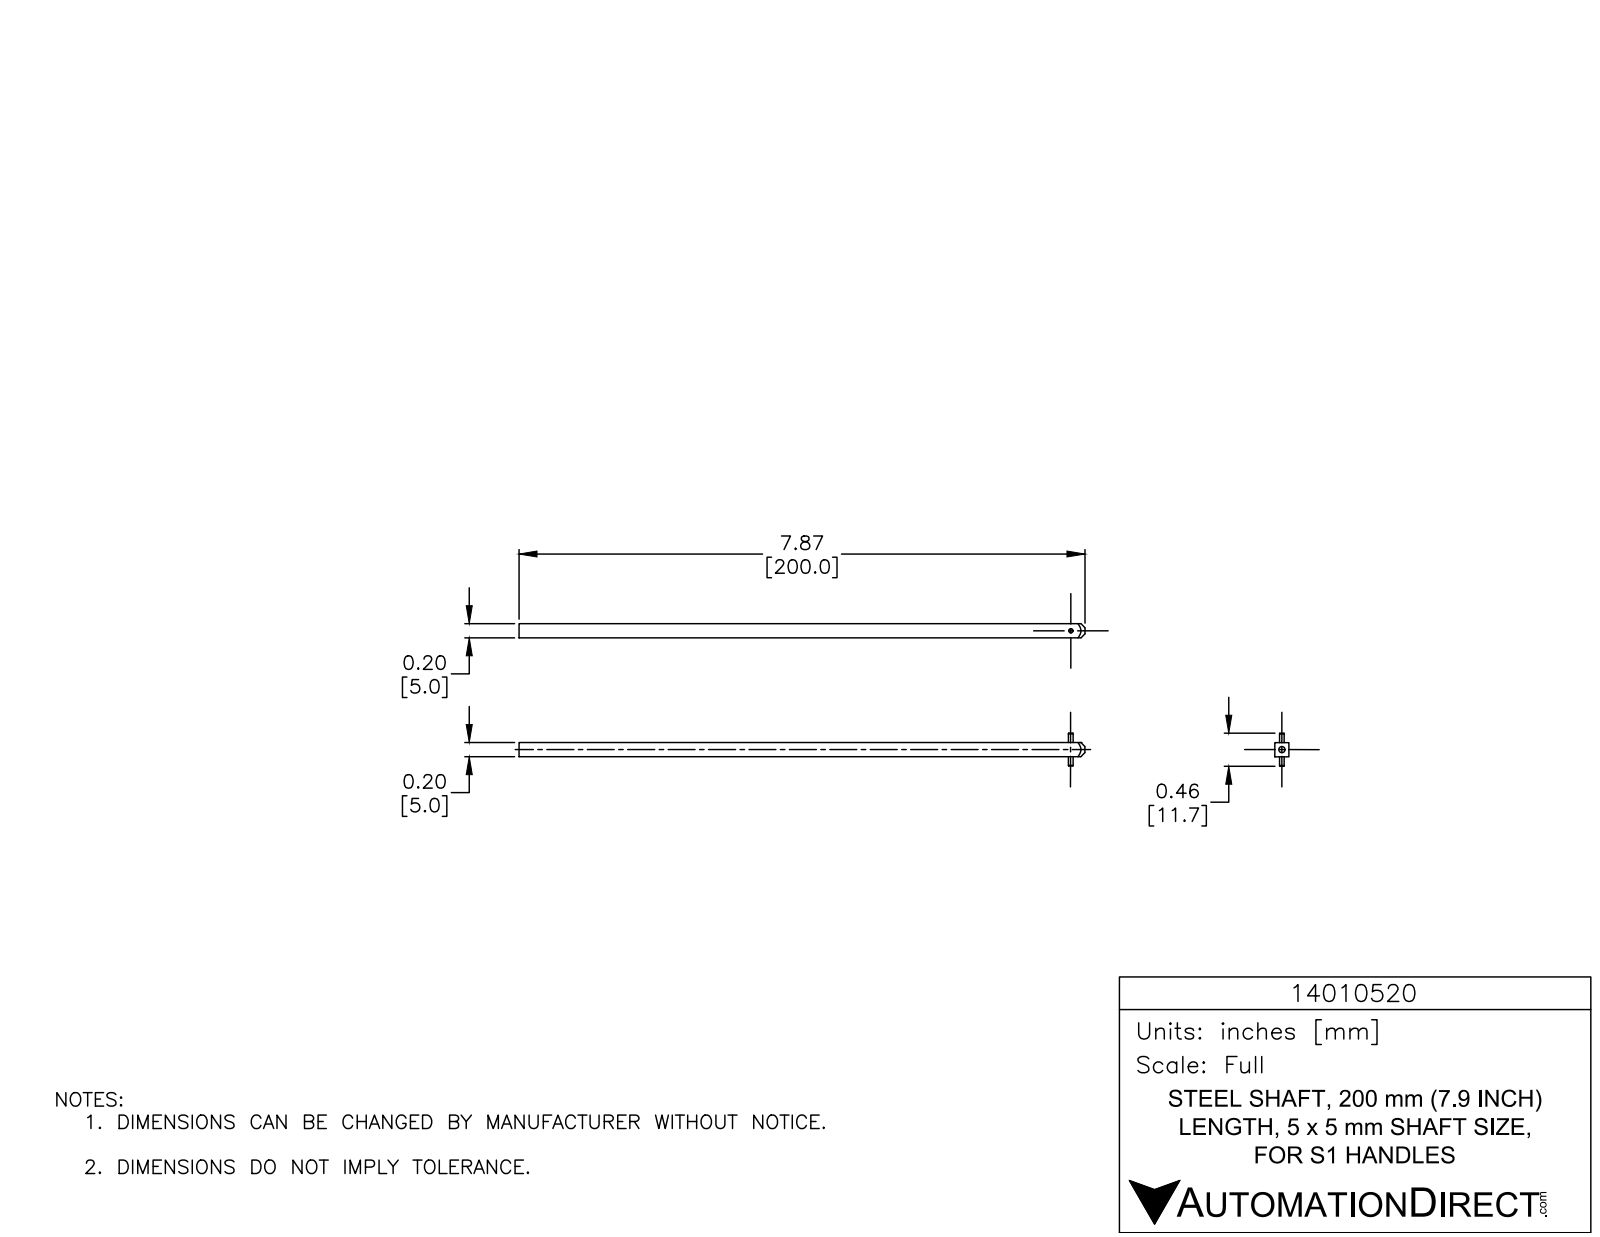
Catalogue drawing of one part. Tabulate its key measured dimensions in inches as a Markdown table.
| quantity | value |
| --- | --- |
| part name | 14010520 |
| STEP written by | SolidWorks 2015 (AUTOMOTIVE_DESIGN) |
| units | inches |
| bodies | 1 solid, 72 faces (35 planar, 24 cylindrical, 13 other) |
| overall size | 7.874 × 0.787 × 0.677 |
| volume | 0.695 in³ |
| surface area | 8.964 in² |
| round bosses / shafts (diameter × count) | 0.118 × 1 |
| partial cylindrical surfaces (radius × count) | 0.012 × 4, 0.118 × 4, 0.039 × 2, 0.335 × 2, 0.063 × 1, 0.138 × 1 |
| main face-to-face distances | 0.197, 0.295, 0.098, 0.394, 0.102, 0.201, 0.398, 0.496, 0.512, 0.118 |
